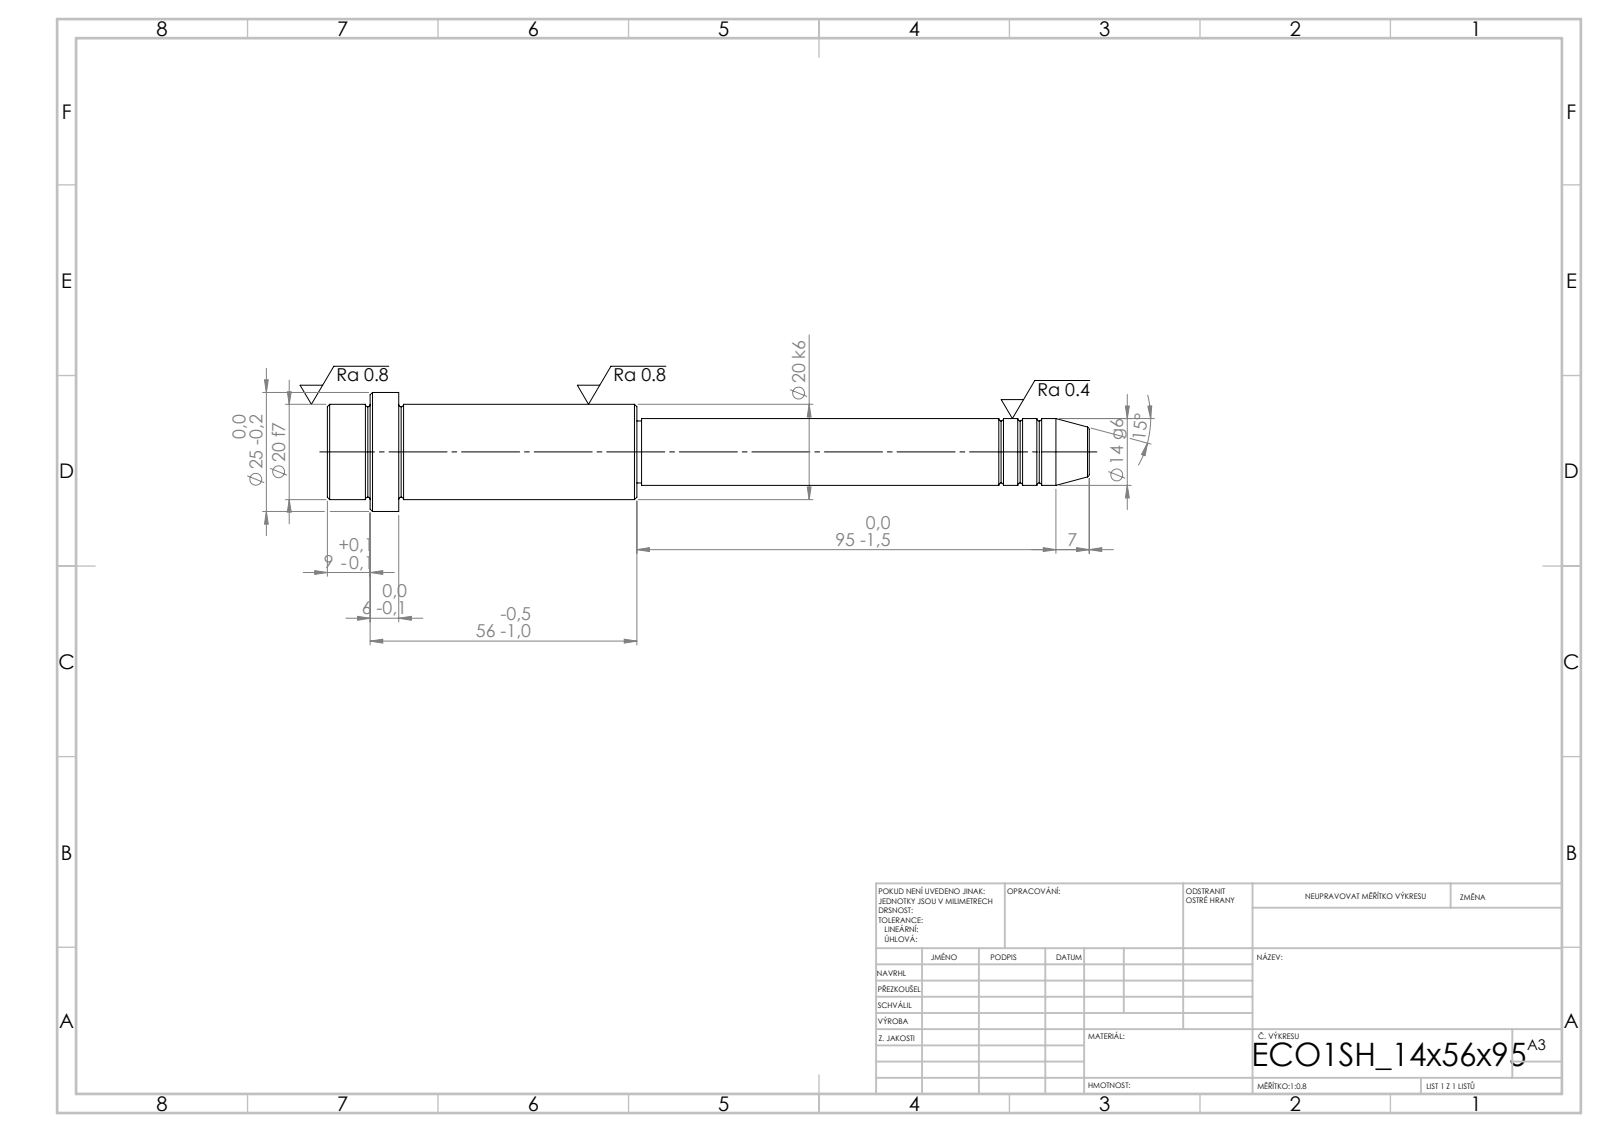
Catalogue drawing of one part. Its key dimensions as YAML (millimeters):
step_written_by: "SolidWorks 2019 (CONFIG_CONTROL_DESIGN)"
units: millimeters
bodies: {solids: 1, faces: 52, planar: 6, cylindrical: 16, other: 30}
overall_size: [160, 25, 25]
volume: 35696
surface_area: 9341
round_bosses_or_shafts:
  - {diameter: 25, count: 1}
  - {diameter: 20, count: 1}
  - {diameter: 14, count: 1}
  - {diameter: 13, count: 1}
face_to_face_distances: [15, 50, 65, 56, 6, 9, 95, 145, 151, 160]
